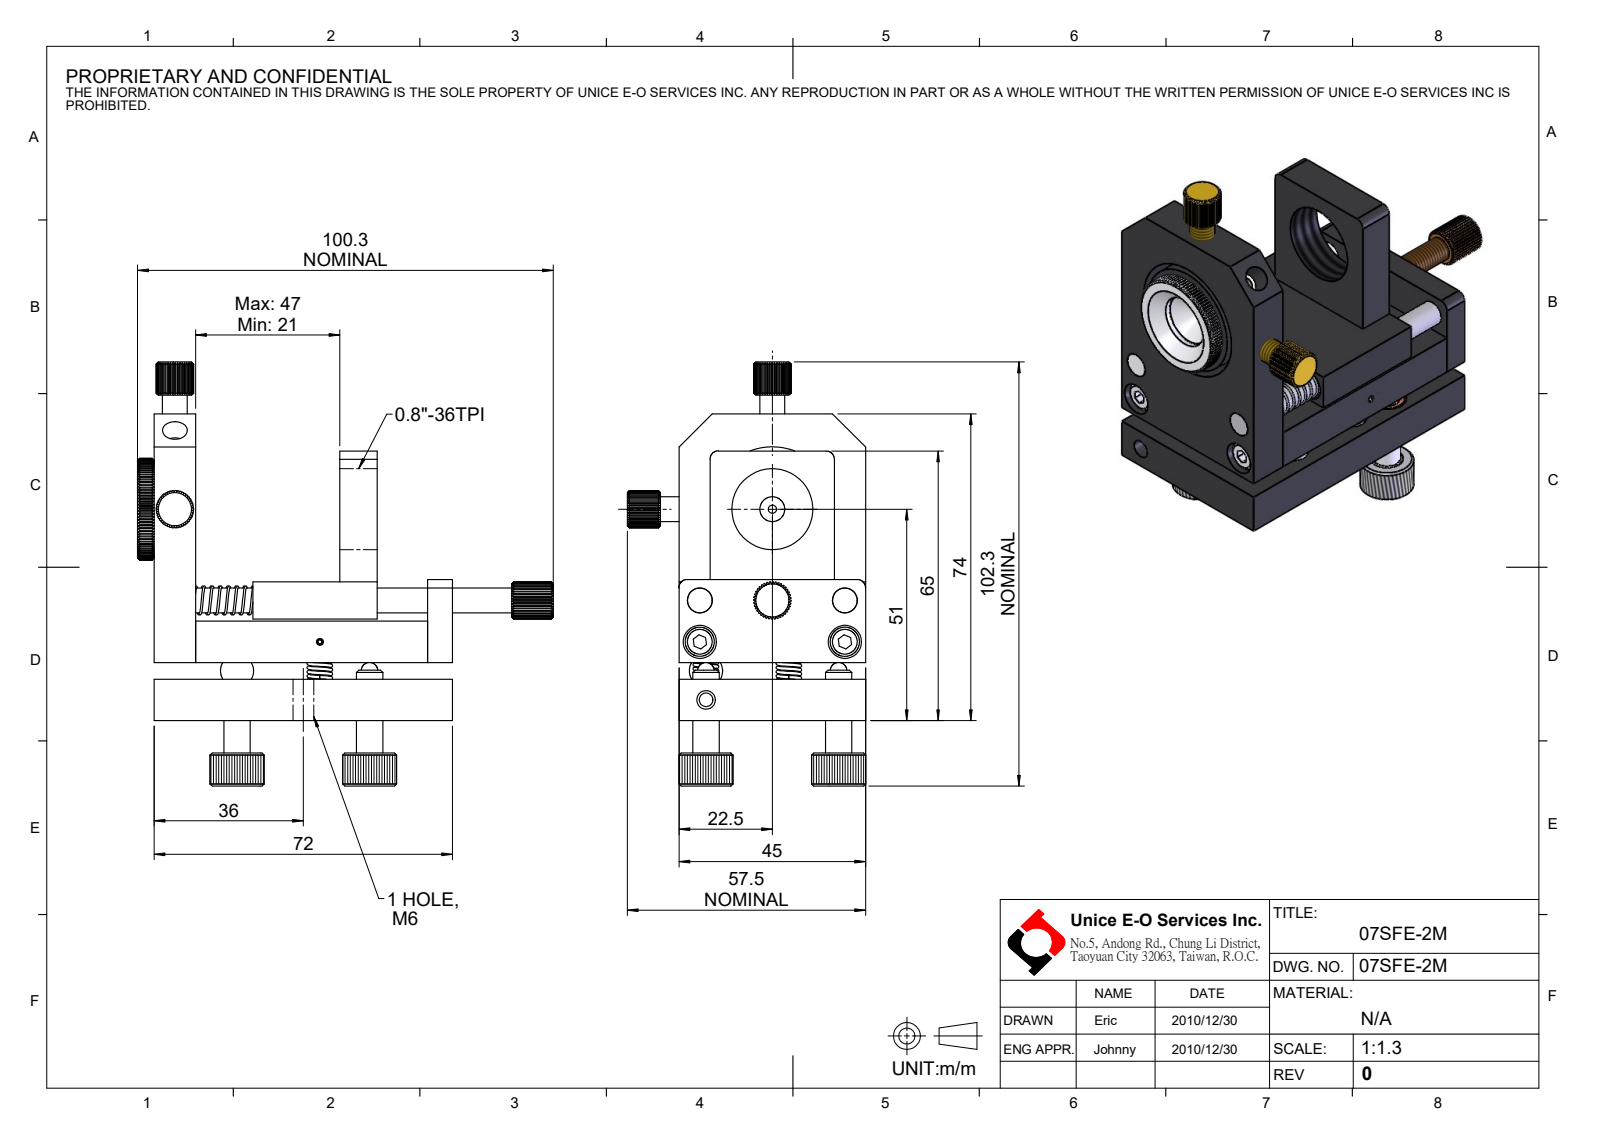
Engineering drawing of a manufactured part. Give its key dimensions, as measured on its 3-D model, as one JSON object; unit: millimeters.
{"part_name": "07SFE-2M", "step_written_by": "SolidWorks 2016 (CONFIG_CONTROL_DESIGN)", "units": "millimeters", "bodies": {"solids": 40, "faces": 1874, "planar": 647, "cylindrical": 462, "other": 765}, "overall_size": [102.3, 100.3, 57.5], "volume_mm3": 107060, "surface_area_mm2": 56173, "round_holes": [[3.3, 6], [4.5, 6], [8, 6], [5, 5], [6, 5], [1, 4], [4, 3], [1.7, 2], [7, 2], [7.9, 2], [9.5, 2], [1.6, 1]], "round_bosses_or_shafts": [[6, 4], [1.3, 4], [0.8, 4], [13, 2], [8, 2], [7, 2], [6.35, 2], [4, 2]], "partial_cylinders_radius": [[0.75, 4], [1, 4], [2, 4], [4.5, 3], [1.5, 1], [12.25, 1]], "face_to_face_distances": [10, 14, 4, 24, 9, 45, 9.5, 66, 6, 19.5], "hole_center_spacings": [10, 15.52, 8.65, 10.77, 12, 14.08, 16, 16.49]}
